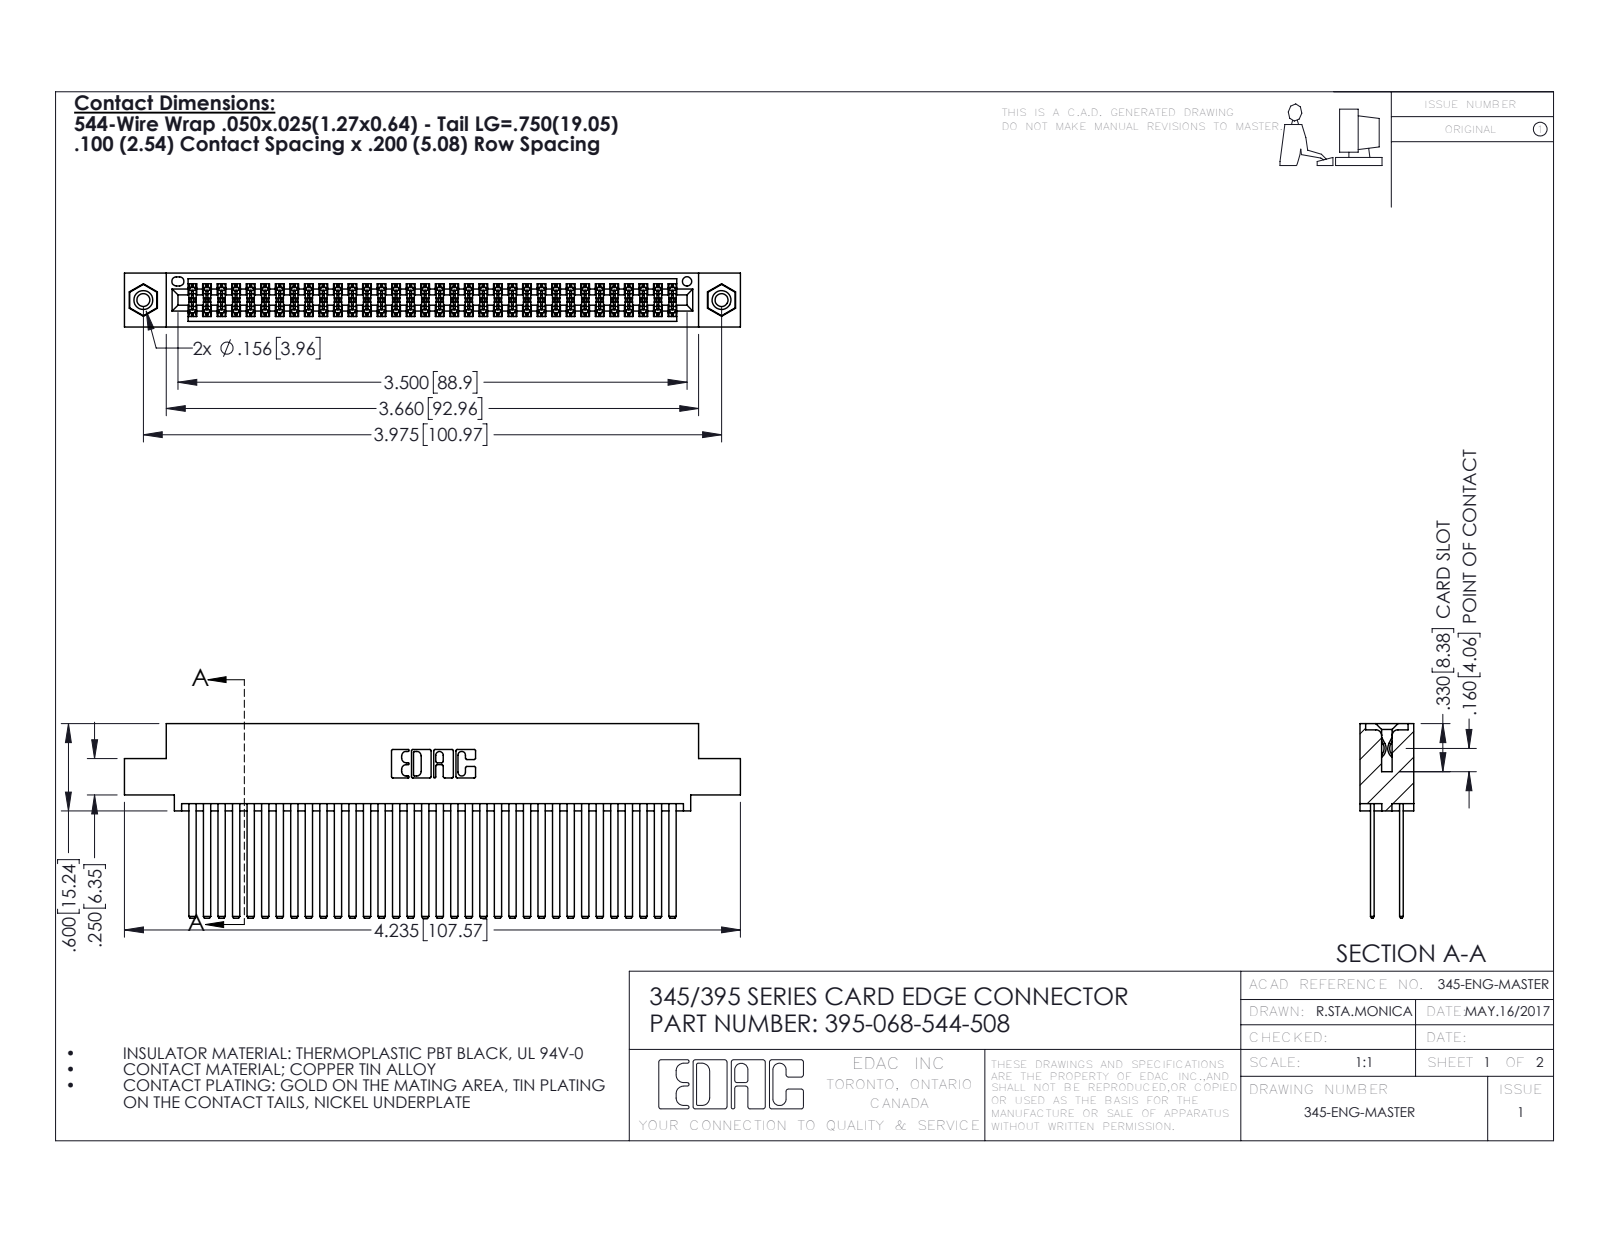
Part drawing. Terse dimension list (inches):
name: 345-292-001_345-293-144; 345-250-001_345-250-003-102; 345 Part_0.110 Offset - 0.156 Dia-TI; 395-068-544-508
written by: SolidWorks 2016 (CONFIG_CONTROL_DESIGN)
unit: in
bodies: 71 solids, 3182 faces (2088 planar, 1078 cylindrical, 16 other)
size: 4.235 × 1.337 × 0.37
volume: 0.686 in³; area: 30.03 in²
holes: 2× ⌀0.089, 2× ⌀0.125, 2× ⌀0.156, 1× ⌀0.064
bosses: 2× ⌀0.155
rounds: 102× R0.006, 22× R0.01, 6× R0.007, 6× R0.031, 3× R0.026, 2× R0.014, 2× R0.019, 2× R0.022
face distances: 0.2, 0.025, 0.072, 0.098, 0.272, 0.298, 0.225, 0.175, 0.37, 0.05
hole spacings: 0.27, 3.74, 3.975
